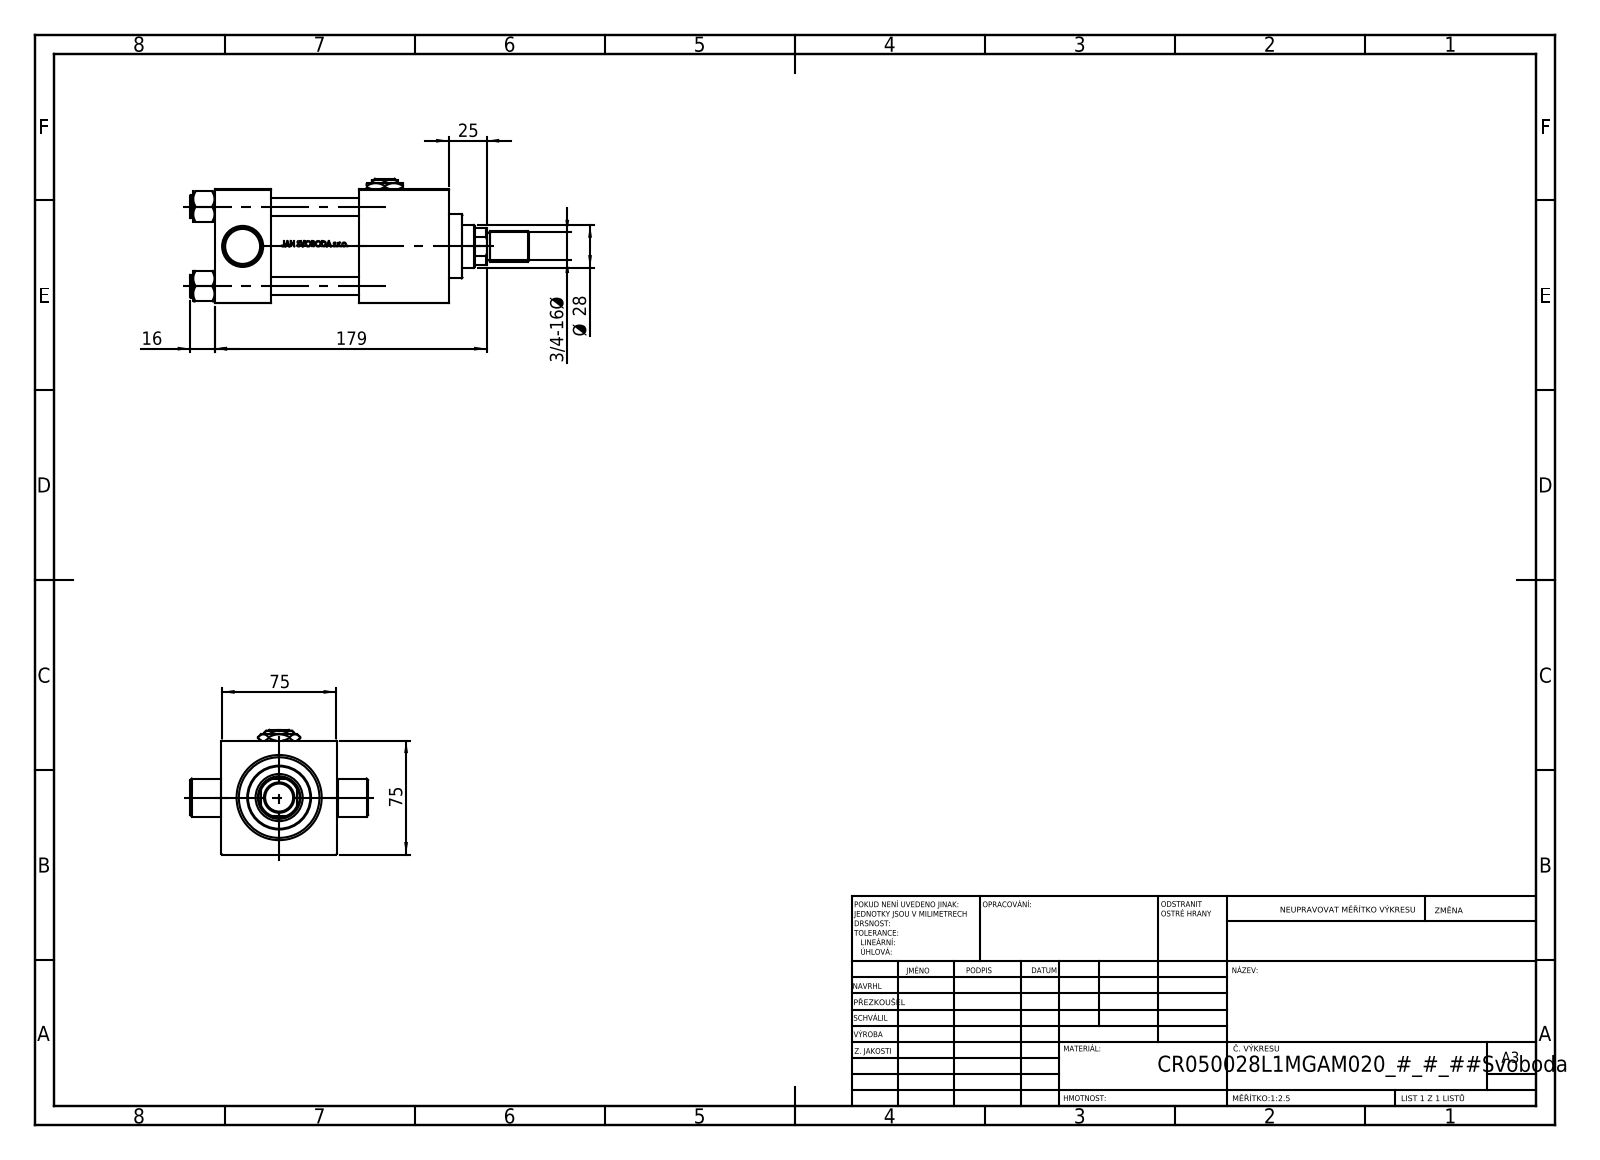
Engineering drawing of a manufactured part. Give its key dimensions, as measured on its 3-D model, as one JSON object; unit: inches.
{"part_name": "V215CR_VCP_L; V215CR_L_TYCINKA; Zatka_pro_OIL_PORT; ROD_END_AH (+3 more)", "step_written_by": "SolidWorks 2019 (CONFIG_CONTROL_DESIGN)", "units": "inches", "bodies": {"solids": 13, "faces": 1133, "planar": 455, "cylindrical": 128, "other": 550}, "overall_size": [8.78, 4.606, 3.228], "volume_in3": 43.18, "surface_area_in2": 238.1, "round_holes": [[0.472, 4], [0.276, 2], [0.825, 2], [1.181, 2], [0.728, 1], [1.102, 1], [1.22, 1], [1.614, 1], [1.969, 1], [2.087, 1]], "round_bosses_or_shafts": [[0.591, 4], [2.205, 1], [1.654, 1], [0.984, 1], [0.787, 1], [0.709, 1]], "partial_cylinders_radius": [[0.531, 1]], "face_to_face_distances": [2.953, 1.457, 0.02, 4.606, 2.992, 2.972, 6.063, 2.283, 2.323, 3.74], "hole_center_spacings": [1.456, 2.059, 2.912, 3.681]}
